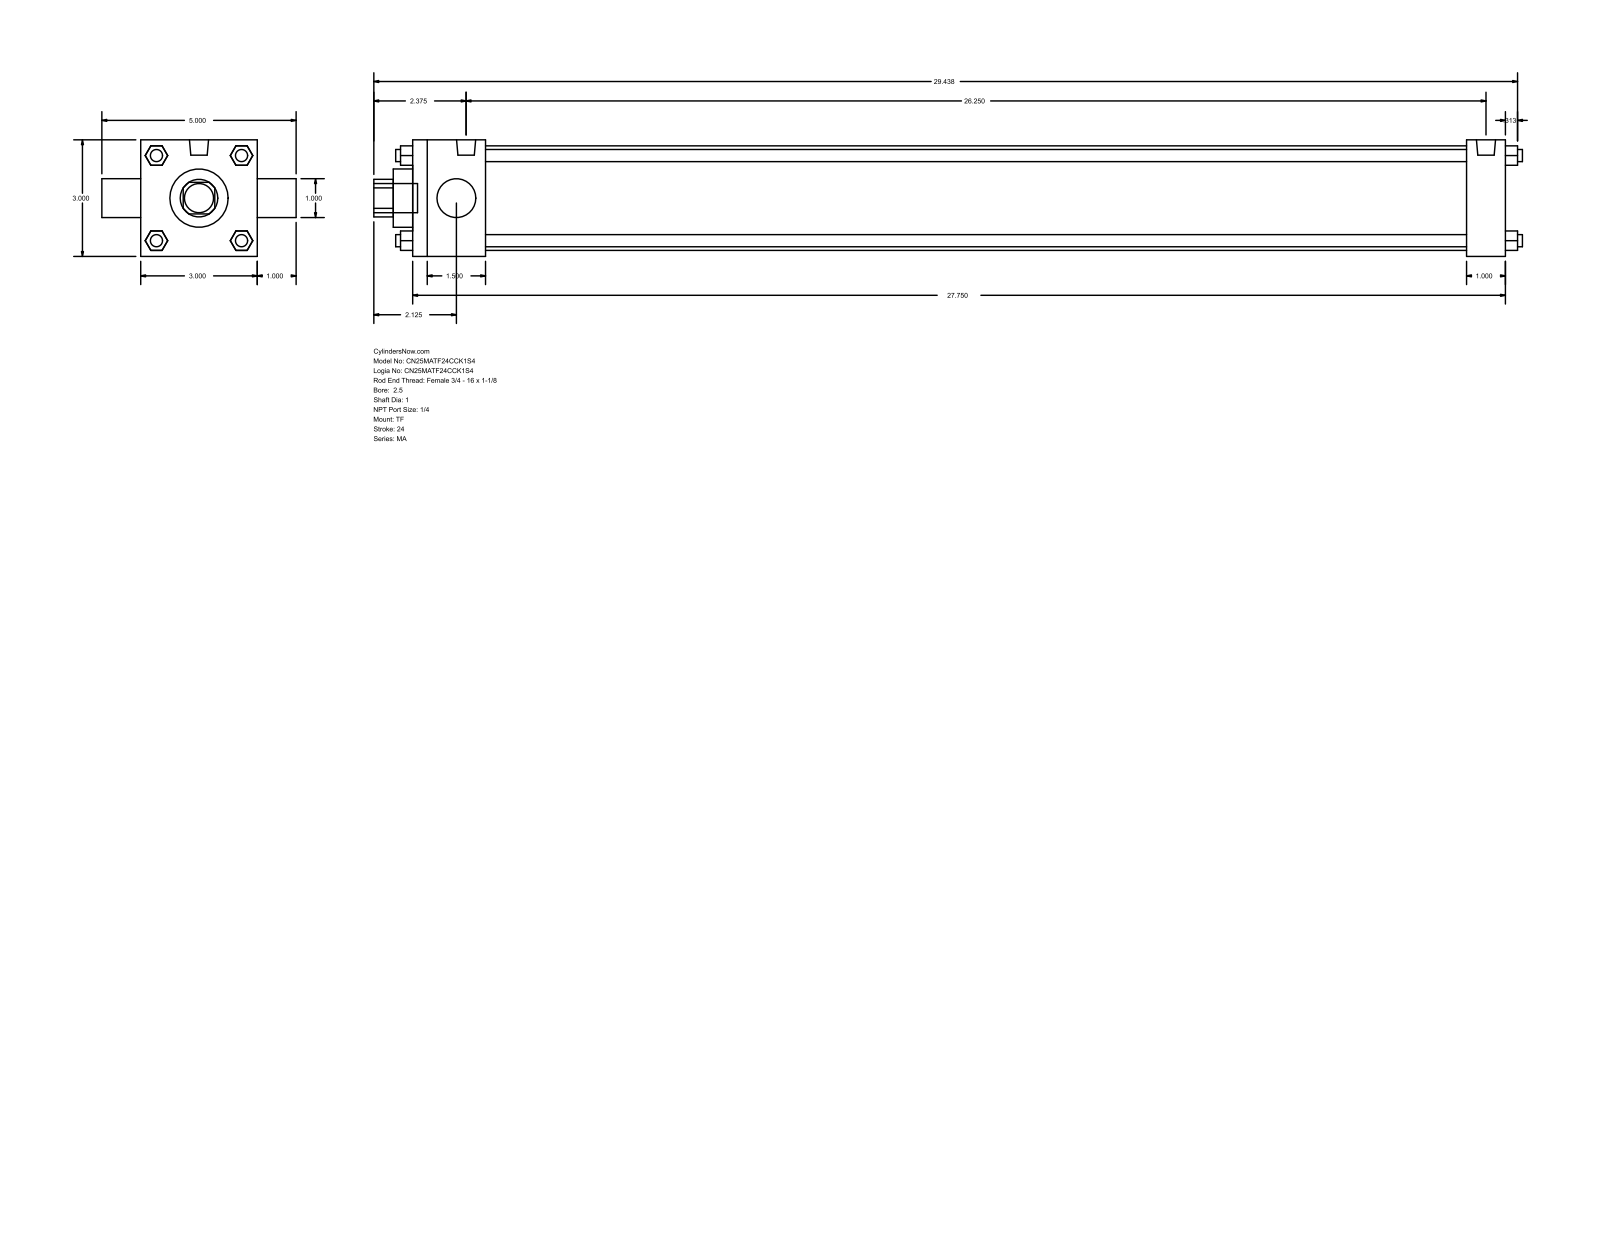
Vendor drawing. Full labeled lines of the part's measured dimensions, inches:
Part name (STEP PRODUCT): MA_TF__0250_1
STEP written by: GSSL Pune (CONFIG_CONTROL_DESIGN)
Units: inches
Bodies: 0 solids, 120 faces (92 planar, 28 cylindrical, 0 other)
Overall size (bounding box): 29.563 × 5 × 3
Round holes (diameter × count): ⌀1 ×2, ⌀1.5 ×1, ⌀2.69 ×1
Round bosses / shafts (diameter × count): ⌀0.313 ×7, ⌀0.492 ×2, ⌀0.75 ×1
Partial cylindrical surfaces — rounded edges, fillets, slot ends (radius × count): R0.484 ×1
Main face-to-face distances: 3, 28.125, 0.5, 1.875, 27.125, 25.25, 26.25, 1, 1, 4
